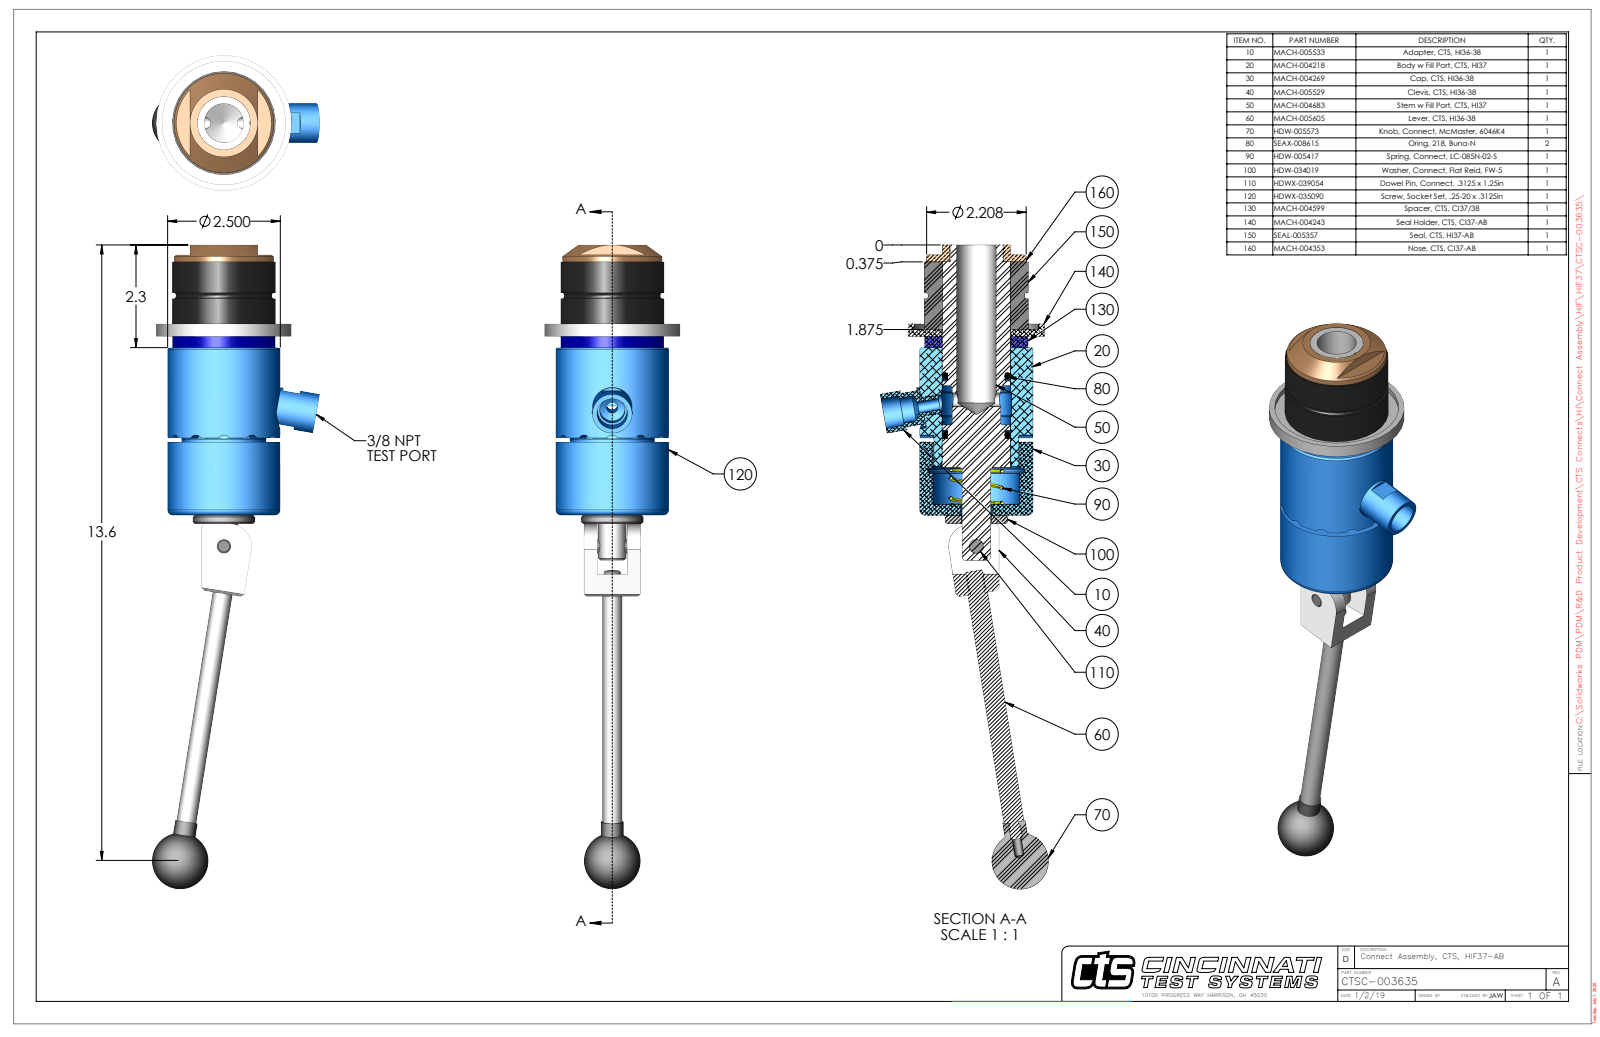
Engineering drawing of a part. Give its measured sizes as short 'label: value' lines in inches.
name: CTSC-003635
written by: SolidWorks 2023 (AUTOMOTIVE_DESIGN)
unit: in
bodies: 10 solids, 312 faces (111 planar, 130 cylindrical, 71 other)
size: 14.275 × 3.716 × 3
volume: 29.14 in³; area: 155.5 in²
holes: 2× ⌀0.201, 1× ⌀0.15, 1× ⌀0.25, 1× ⌀0.311, 1× ⌀0.312, 1× ⌀0.313, 1× ⌀0.314, 1× ⌀0.562, 1× ⌀0.656, 1× ⌀0.696, 1× ⌀0.875, 1× ⌀1.172
bosses: 1× ⌀3, 1× ⌀2.5, 1× ⌀2.295, 1× ⌀2.281, 1× ⌀2.208, 1× ⌀1.875, 1× ⌀1.5, 1× ⌀1.496
rounds: 12× R0.12, 2× R0.029, 1× R0.19, 1× R0.195, 1× R0.47, 1× R0.473, 1× R0.5, 1× R1.198
face distances: 0.152, 1.5, 1.652, 0.25, 0.402, 1.902, 3.713, 3.963, 4.115, 5.615
hole spacings: 0.74, 2.118, 2.858
